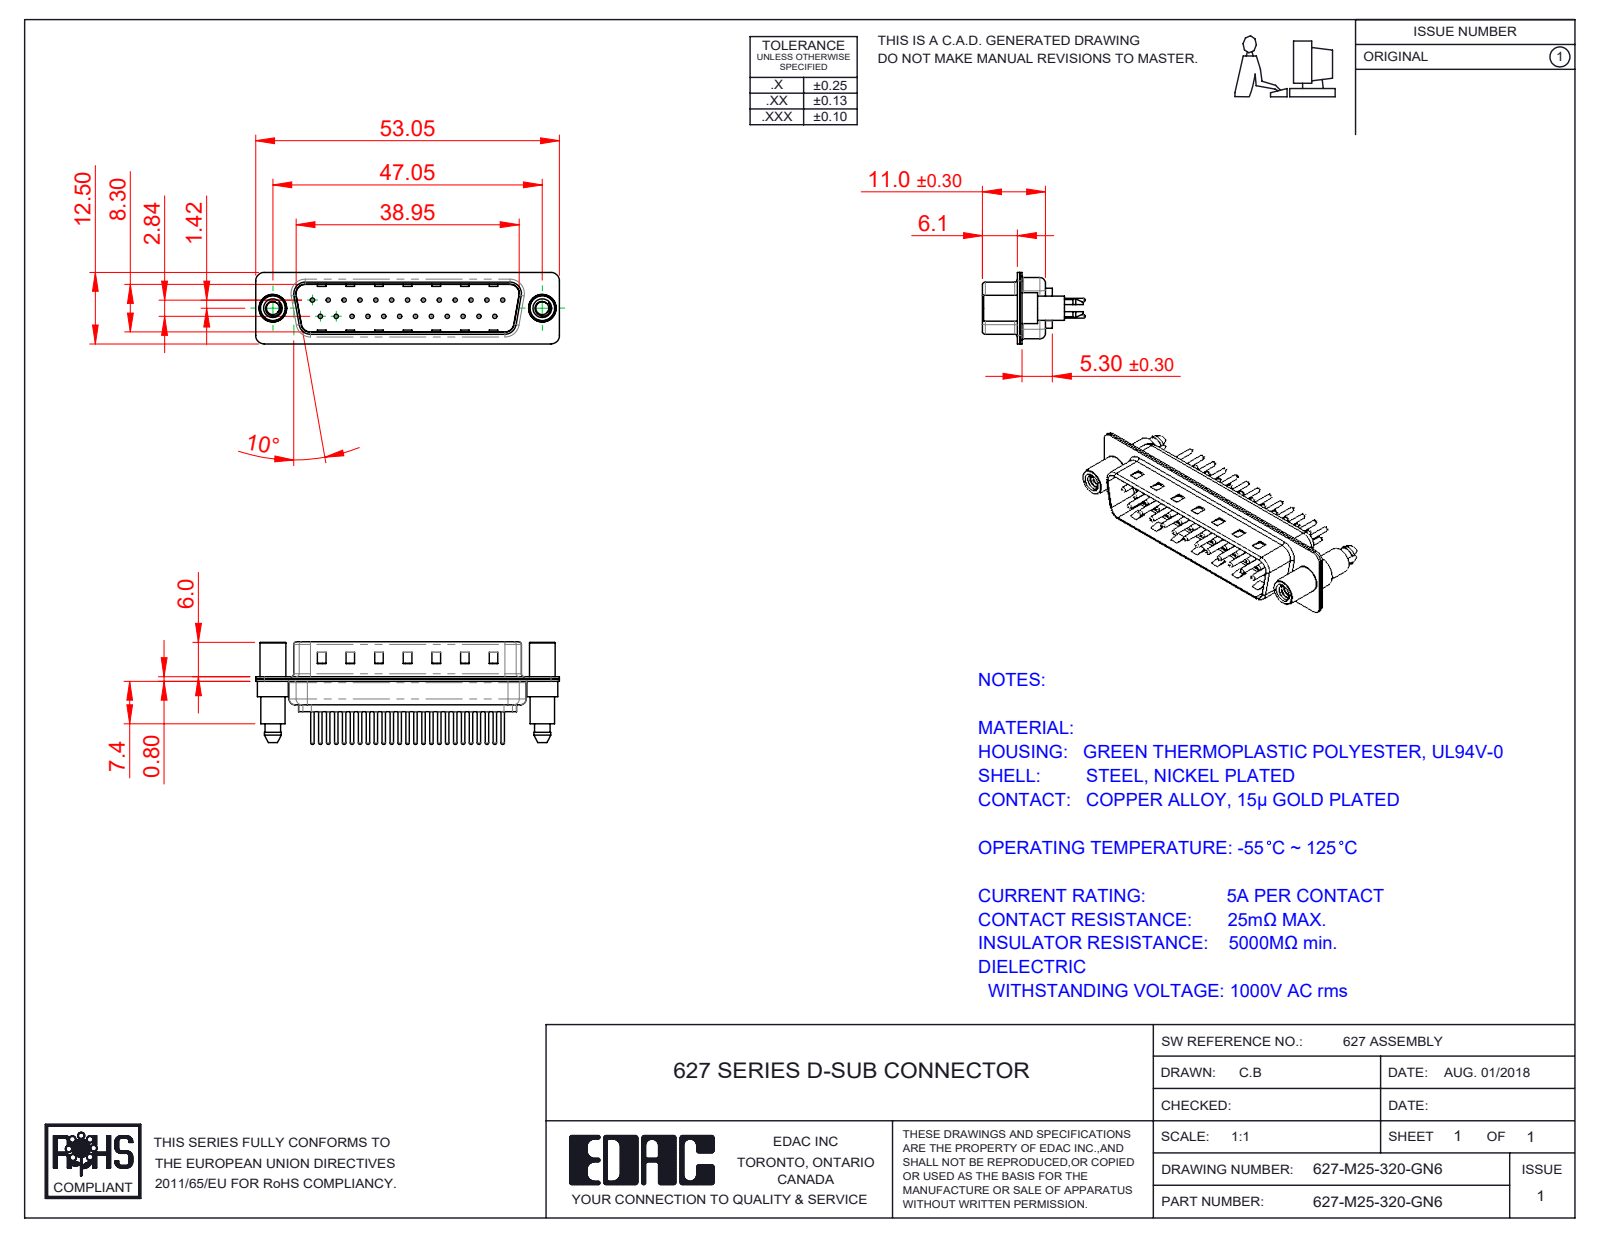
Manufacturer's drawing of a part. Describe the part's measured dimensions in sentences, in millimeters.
The part is named "627M 4-40 Threaded Standoff and Boardlock; 627-M25-320-GN6; 627M Contact Row 2_20; 627M Housing_25 Contacts (+3 more)". Its 3-D file was written by "SolidWorks 2020 (CONFIG_CONTROL_DESIGN)". It is 30 solids with 1353 faces: 364 planar, 515 cylindrical and 474 other. Overall it measures 53.05 by 17.9 by 12.5 millimeters. Its volume is 3 058 cubic millimeters and its surface area 7 311 square millimeters. Round holes: 25 of diameter 0.75, 25 of diameter 1.6, 25 of diameter 2, 2 of diameter 2.26, 2 of diameter 4, 2 of diameter 4.8. Round bosses or shafts: 25 of diameter 1.5, 25 of diameter 0.6, 2 of diameter 5.4, 2 of diameter 4.9, 2 of diameter 4.5, 2 of diameter 4.25. Partial cylindrical surfaces (rounded edges, fillets, slot ends): 18 of radius 1.5, 12 of radius 2, 10 of radius 1.6, 8 of radius 0.5, 4 of radius 0.25, 4 of radius 0.6, 4 of radius 0.65, 4 of radius 0.9. The main face-to-face distances are 0.4, 0.8, 9.5, 9.1, 8.7, 9.9, 1.2, 5.7, 6.1, 0.75. The hole center spacings are 3.16, 2.77, 5.54, 8.31, 11.08, 13.85, 16.62, 5.03.
